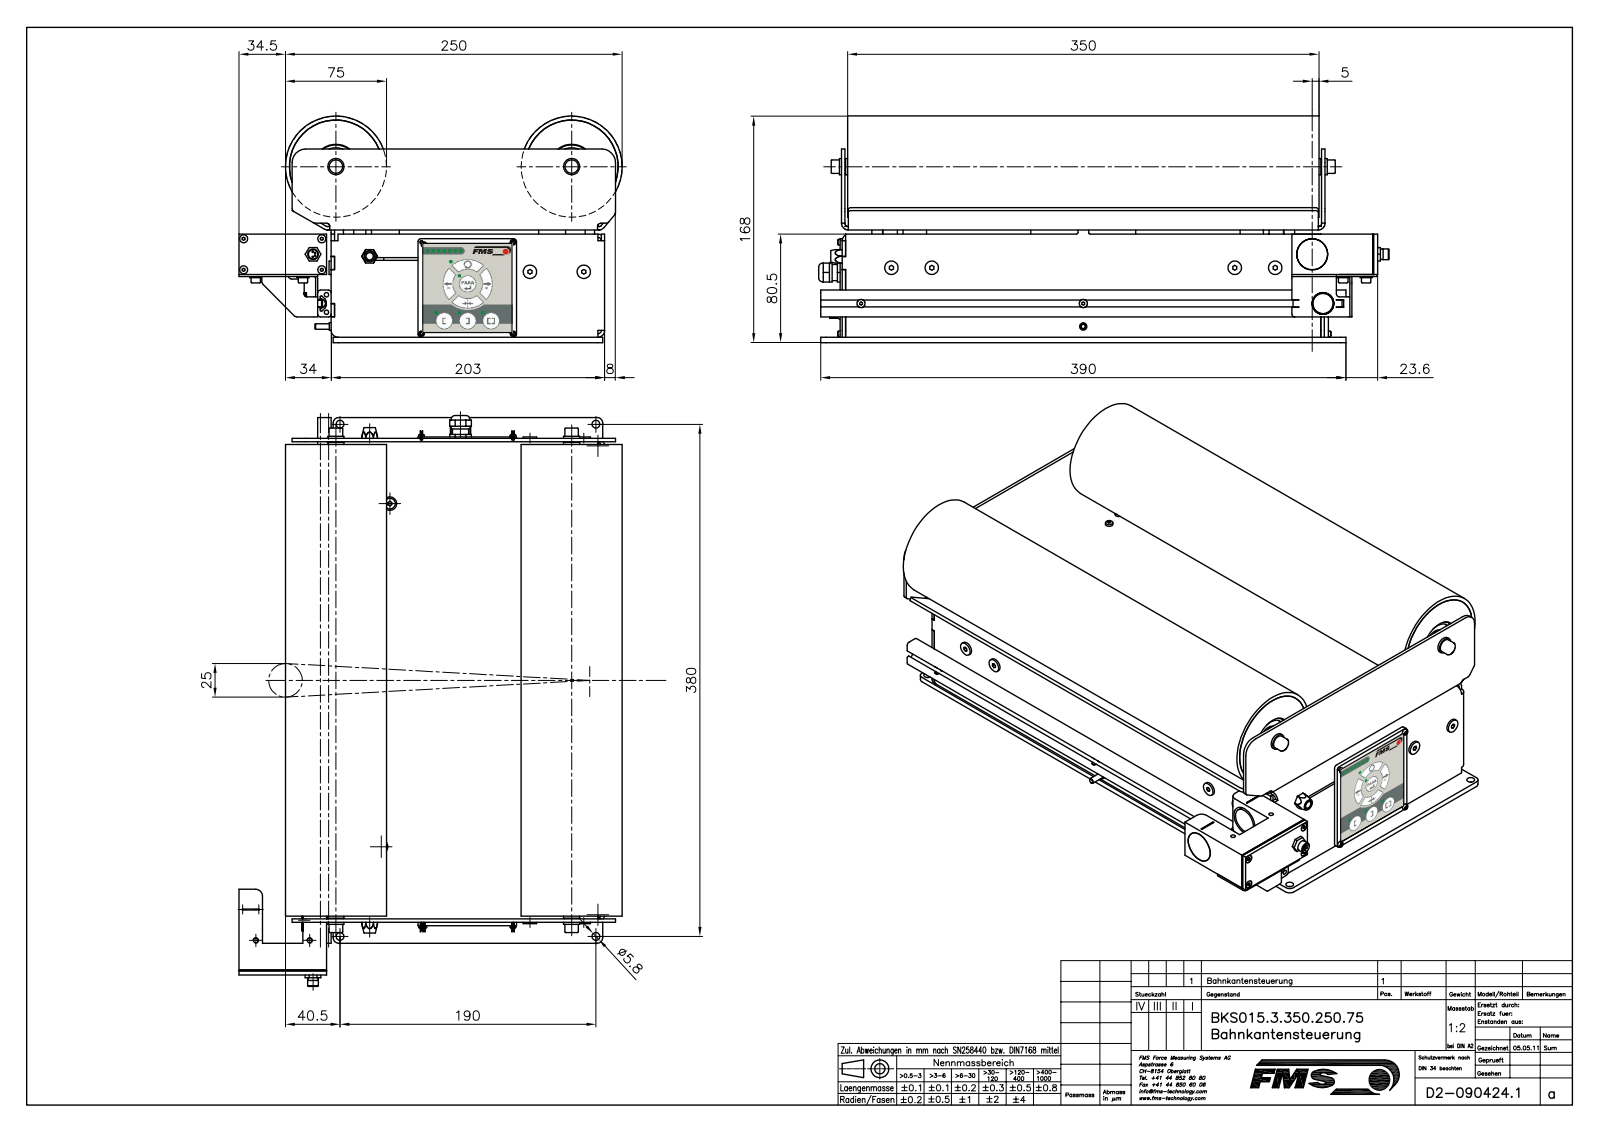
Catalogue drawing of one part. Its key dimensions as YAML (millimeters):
part_name: "K0904241; K0904248; K0904249; K0904252 (+8 more)"
step_written_by: "Mechanical Desktop 2009 (CONFIG_CONTROL_DESIGN)"
units: millimeters
bodies: {solids: 1313, faces: 21539, planar: 14471, cylindrical: 5205, other: 1863}
overall_size: [423.6, 284.5, 168]
volume: 2211000
surface_area: 1345000
round_holes:
  - {diameter: 3.2, count: 35}
  - {diameter: 0.8, count: 30}
  - {diameter: 1, count: 25}
  - {diameter: 2.6, count: 20}
  - {diameter: 1.1, count: 16}
  - {diameter: 3.42, count: 16}
  - {diameter: 4.5, count: 16}
  - {diameter: 6, count: 16}
  - {diameter: 2.14, count: 11}
  - {diameter: 4.3, count: 9}
  - {diameter: 5.3, count: 9}
  - {diameter: 2.5, count: 8}
round_bosses_or_shafts:
  - {diameter: 4, count: 25}
  - {diameter: 8, count: 21}
  - {diameter: 3, count: 21}
  - {diameter: 0.6, count: 20}
  - {diameter: 10, count: 15}
  - {diameter: 6, count: 12}
  - {diameter: 5, count: 12}
  - {diameter: 7, count: 10}
partial_cylinders:
  - {radius: 0.25, count: 104}
  - {radius: 0.1, count: 84}
  - {radius: 0.2, count: 80}
  - {radius: 0.15, count: 70}
  - {radius: 0.25, count: 60}
  - {radius: 2.5, count: 42}
  - {radius: 0.3, count: 41}
  - {radius: 0.56, count: 36}
face_to_face_distances: [2.5, 4, 79.5, 82, 83.5, 86, 0.5, 2, 356, 3]
hole_center_spacings: [66.18, 100, 2.54, 68, 2.62, 5.08, 11.77, 12]
